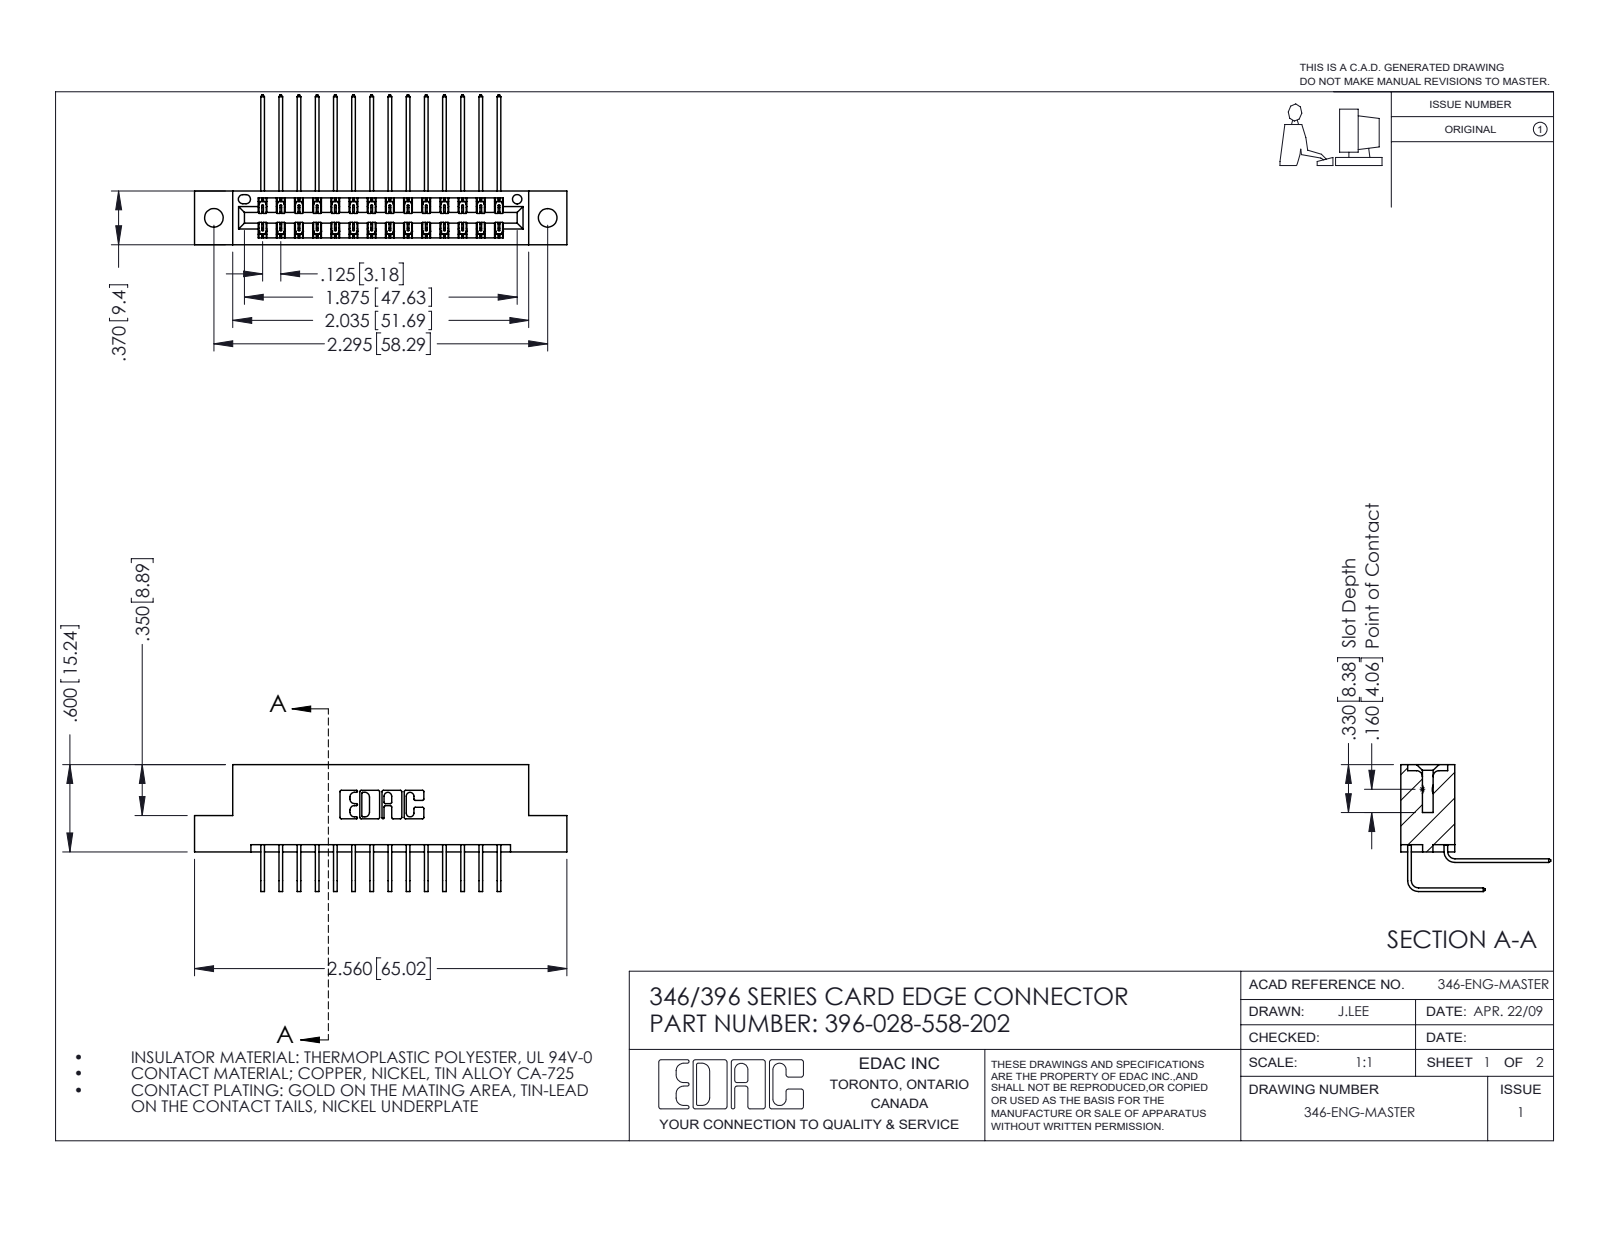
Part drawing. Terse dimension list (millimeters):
name: 396-028-558-202; 345-292-001_558 Tail - 2; 345-292-001_558 559 Tail - 1; 346 Part_Flush Mounting Lugs - 0.128 Dia
written by: SolidWorks 2016 (CONFIG_CONTROL_DESIGN)
unit: mm
bodies: 29 solids, 1634 faces (1112 planar, 522 cylindrical, 0 other)
size: 65 × 26.2 × 22.2
volume: 6 240 mm³; area: 8 652 mm²
holes: 2× ⌀3.3, 1× ⌀1.6
rounds: 42× R0.2, 22× R0.3, 6× R0.2, 6× R0.8, 3× R0.7, 2× R0.4, 2× R0.6, 2× R0.6
face distances: 8.2, 1.2, 6.4, 9.4, 0.6, 7.6, 1.8, 7, 3.8, 5.6
hole spacings: 6.2, 53.1, 58.3
